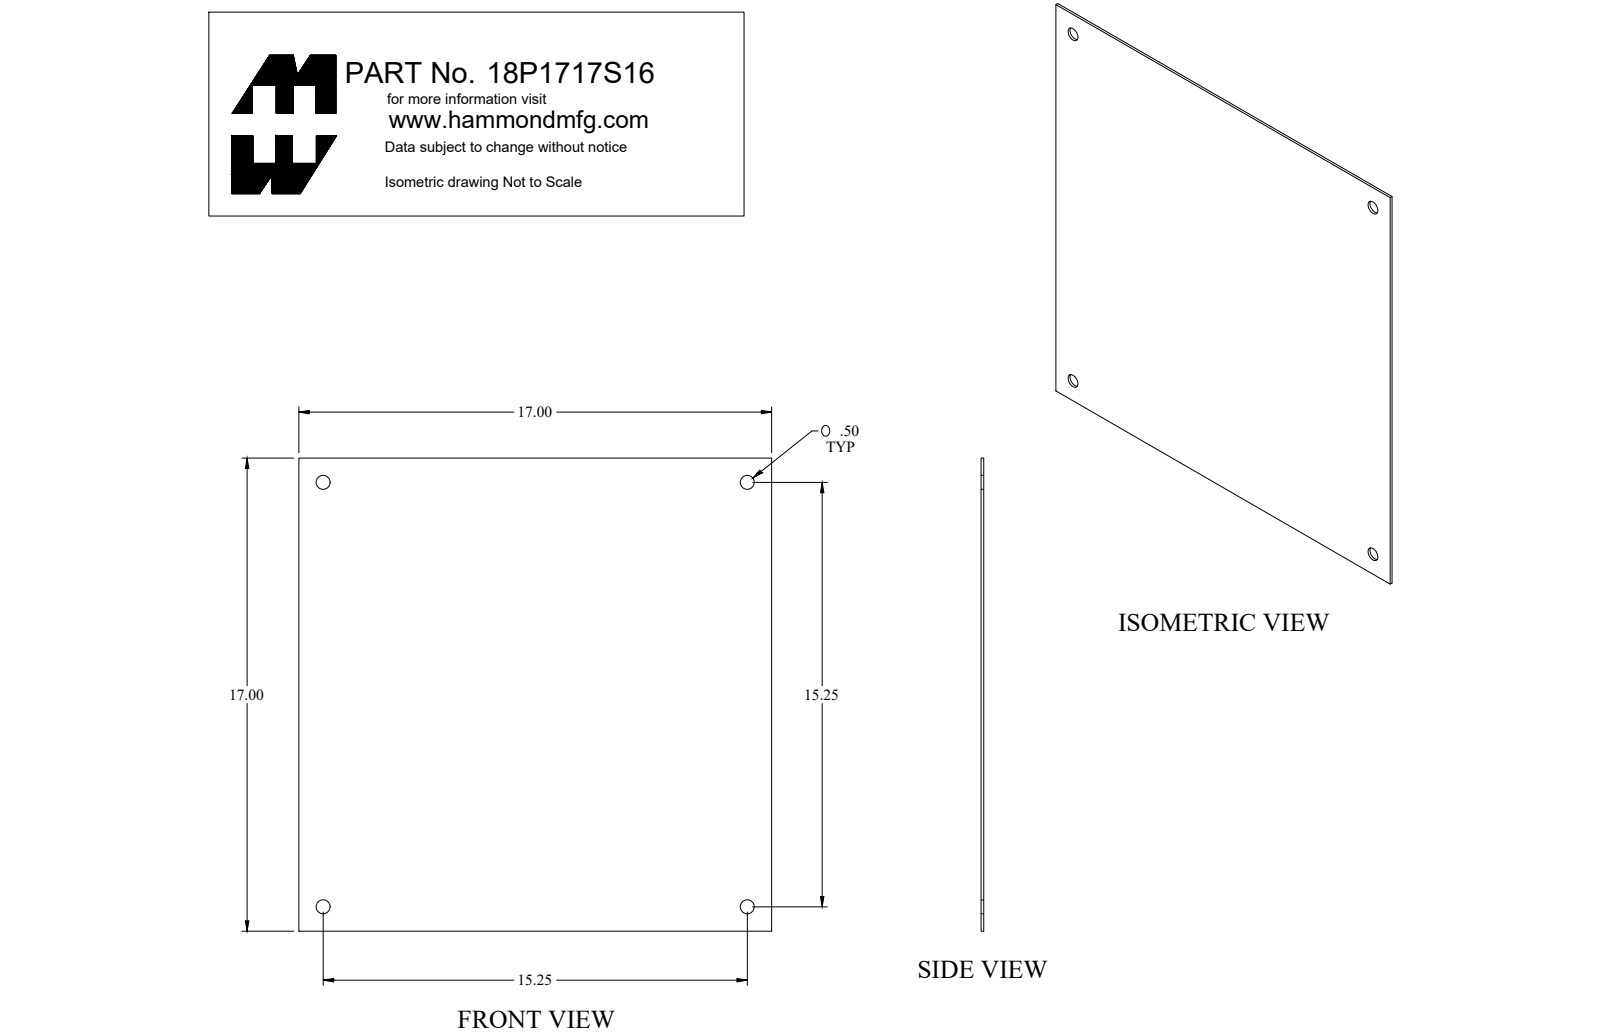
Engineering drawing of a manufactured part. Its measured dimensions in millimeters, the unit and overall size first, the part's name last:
Units: millimetres
Overall size (bounding box): 431.8 × 431.8 × 2.4
Round holes (diameter × count): ⌀12.7 ×4
Main face-to-face distances: 2.4, 431.8
Hole centre spacings: 387.4, 547.8
Volume: 448 700 mm³ · Surface area: 376 500 mm²
Bodies: 1 solid, 14 faces (6 planar, 8 cylindrical, 0 other)
Part name (STEP PRODUCT): 18P1717S16_Default
STEP written by: SolidWorks 2018 (CONFIG_CONTROL_DESIGN)
